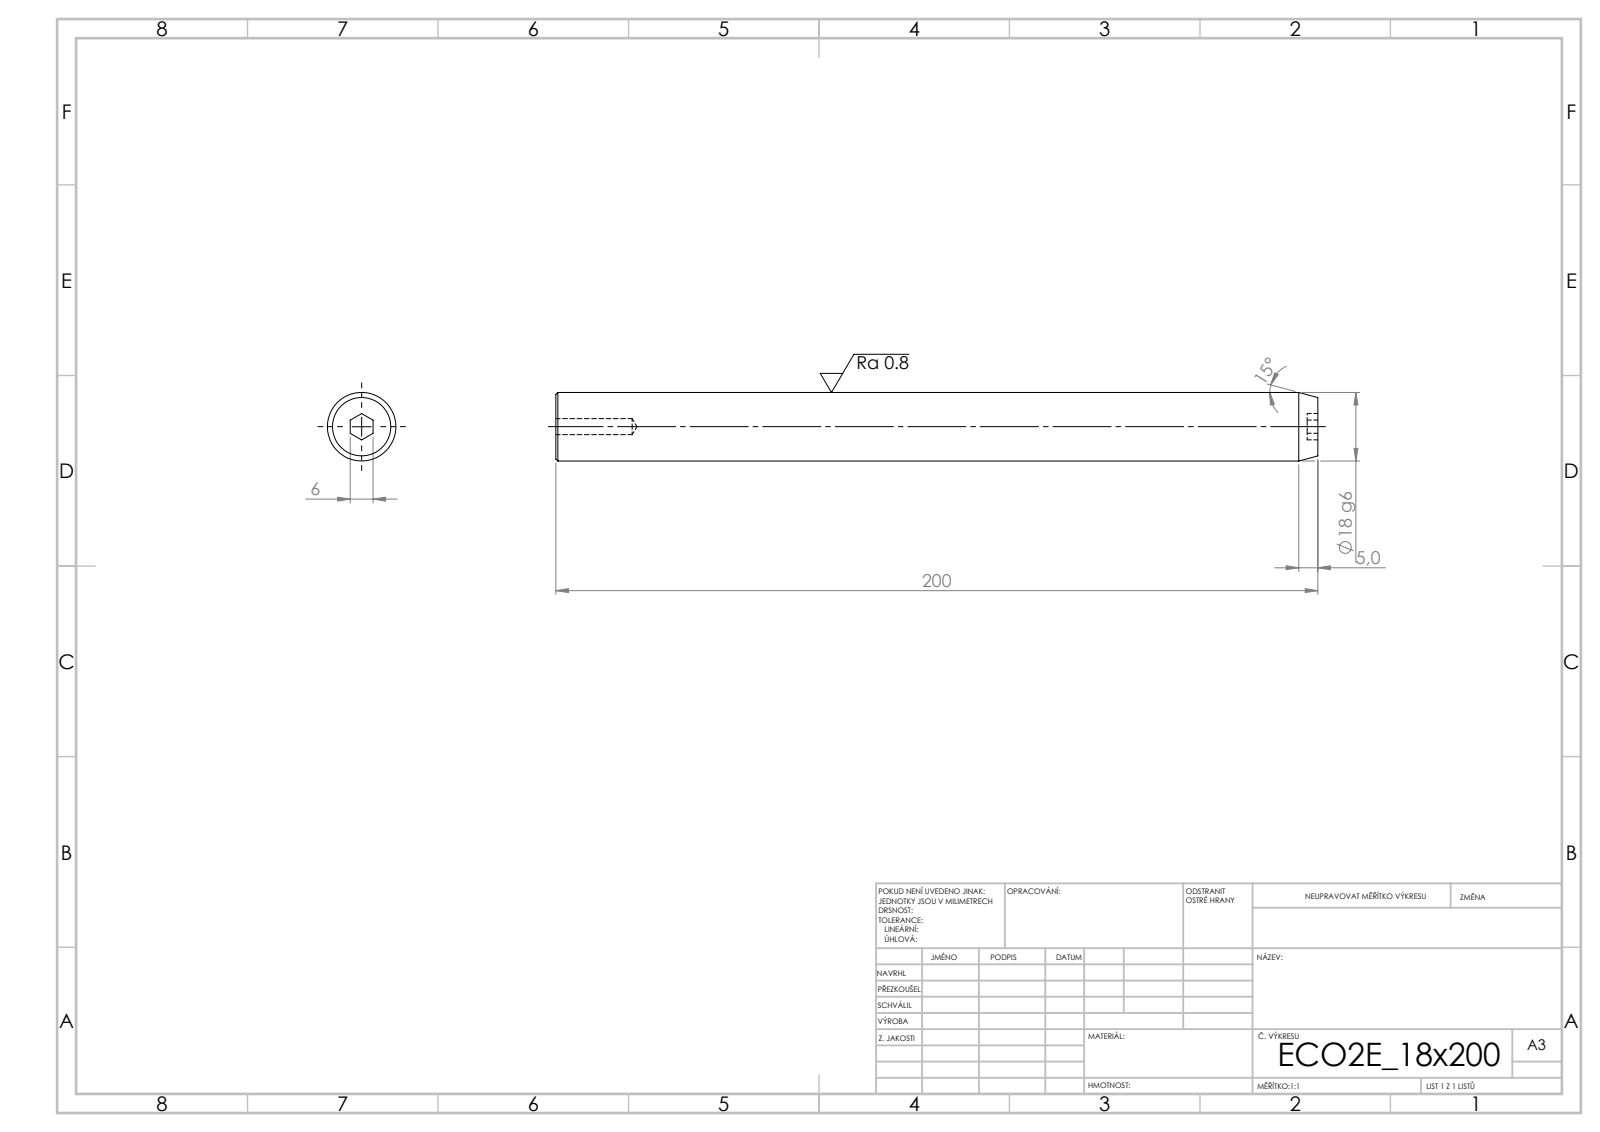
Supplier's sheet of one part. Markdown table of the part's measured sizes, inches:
| quantity | value |
| --- | --- |
| STEP written by | SolidWorks 2019 (CONFIG_CONTROL_DESIGN) |
| units | inches |
| bodies | 1 solid, 19 faces (9 planar, 4 cylindrical, 6 other) |
| overall size | 7.874 × 0.709 × 0.709 |
| volume | 3.072 in³ |
| surface area | 18.67 in² |
| round holes (diameter × count) | 0.165 × 1 |
| round bosses / shafts (diameter × count) | 0.709 × 1 |
| main face-to-face distances | 7.874, 0.11, 7.764, 0.236 |
